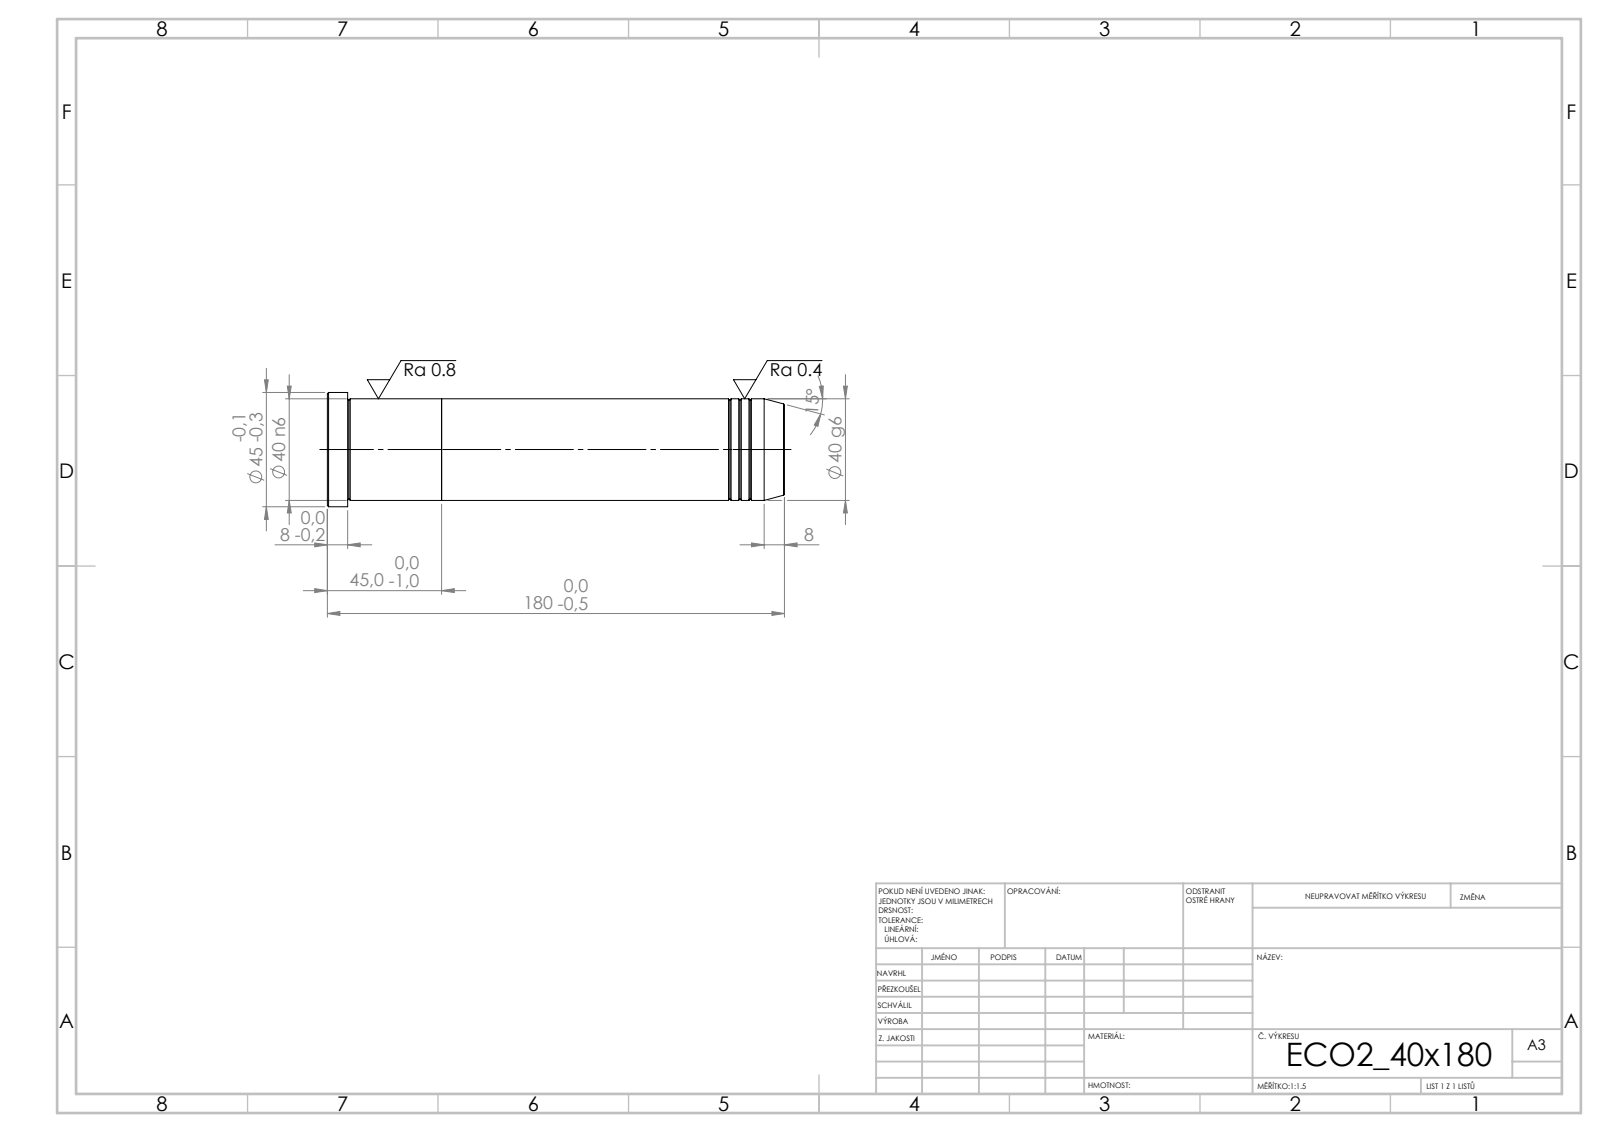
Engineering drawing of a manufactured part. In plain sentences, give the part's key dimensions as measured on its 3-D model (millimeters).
Its 3-D file was written by "SolidWorks 2019 (CONFIG_CONTROL_DESIGN)". It is 2 solids with 39 faces: 5 planar, 12 cylindrical and 22 other. Overall it measures 180 by 45 by 45 millimeters. Its volume is 227 610 cubic millimeters and its surface area 28 384 square millimeters. Round bosses or shafts: 1 of diameter 45, 1 of diameter 40. The main face-to-face distances are 45, 135, 180, 172, 37, 8.
